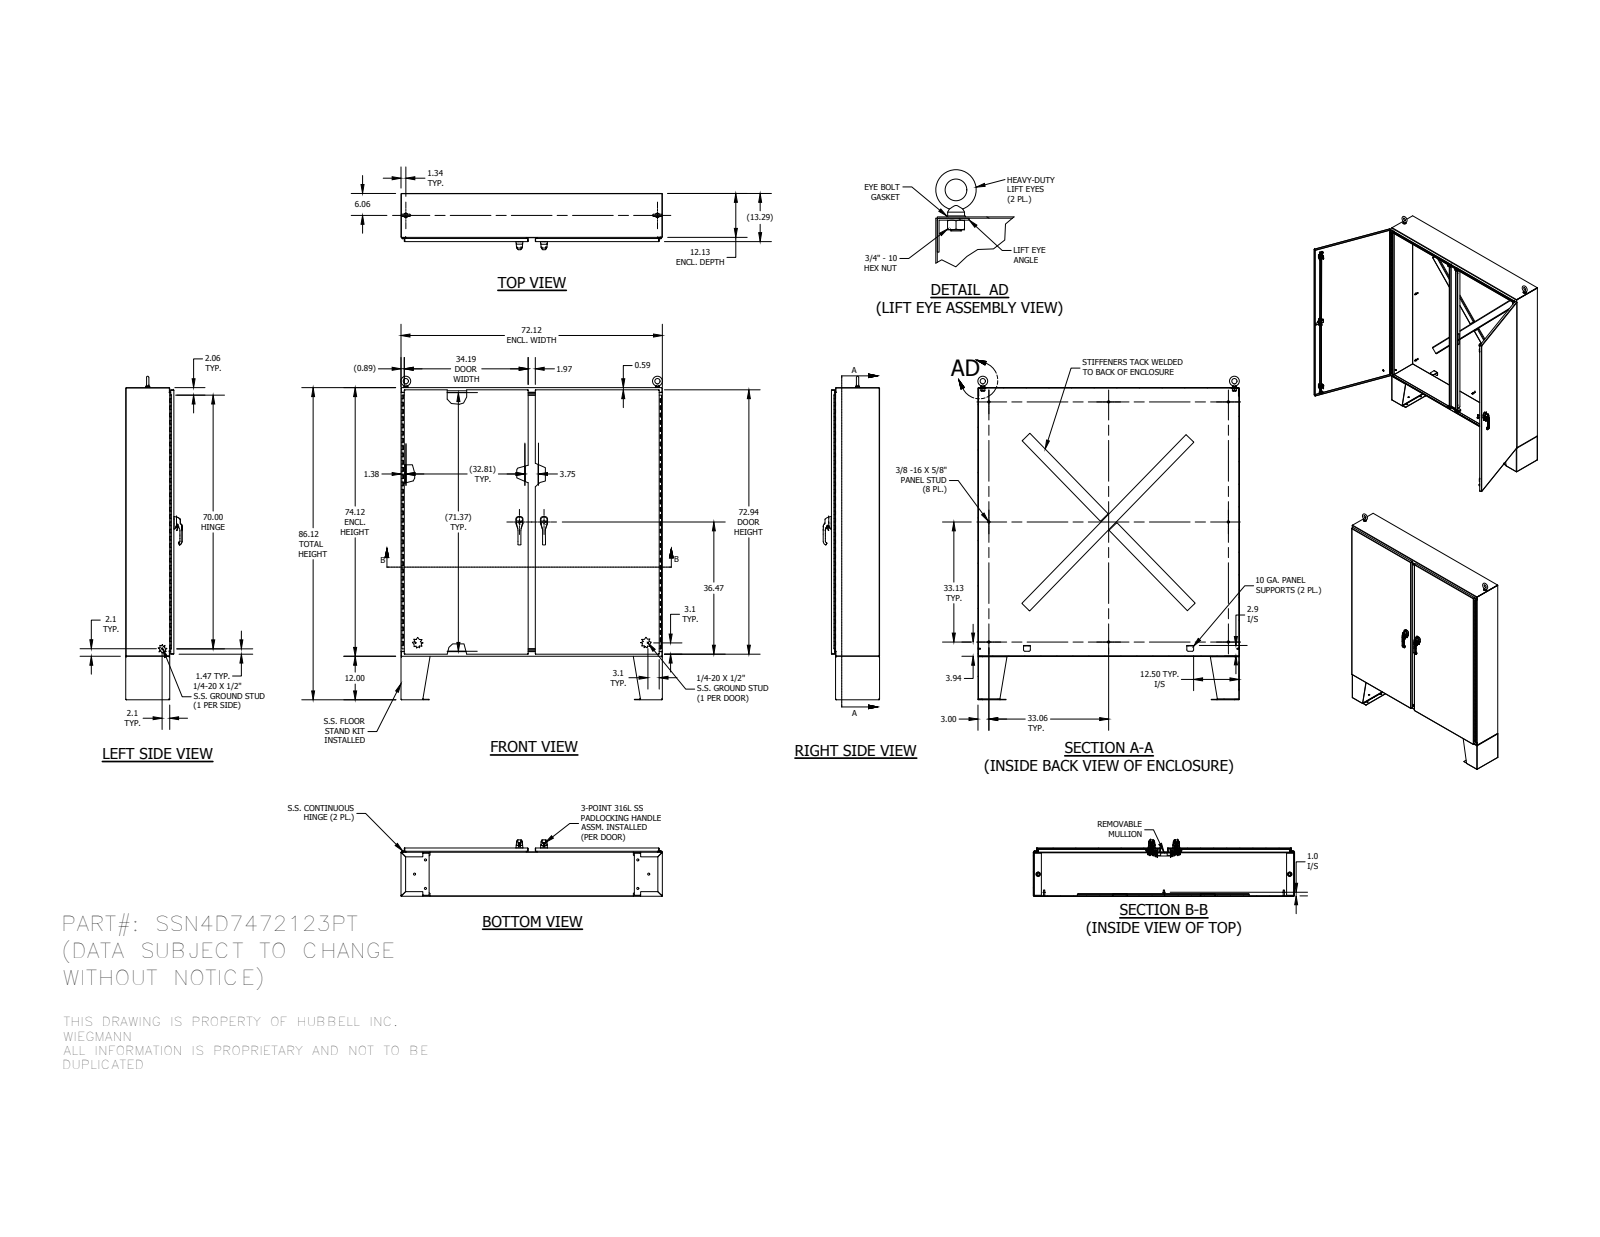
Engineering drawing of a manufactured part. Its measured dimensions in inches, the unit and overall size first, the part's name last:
Units: inches
Overall size (bounding box): 89.248 × 72.125 × 15.538
Round holes (diameter × count): ⌀0.563 ×18, ⌀0.262 ×16, ⌀0.375 ×16, ⌀0.187 ×8, ⌀0.213 ×6, ⌀0.25 ×6, ⌀0.281 ×6, ⌀0.196 ×4, ⌀0.241 ×4, ⌀0.252 ×4, ⌀0.281 ×4, ⌀0.315 ×4
Round bosses / shafts (diameter × count): ⌀0.33 ×10, ⌀0.625 ×8, ⌀0.25 ×7, ⌀1 ×6, ⌀0.533 ×6, ⌀0.236 ×6, ⌀0.563 ×4, ⌀0.531 ×4
Partial cylindrical surfaces — rounded edges, fillets, slot ends (radius × count): R0.02 ×360, R0.012 ×213, R0.019 ×46, R0.125 ×46, R0.05 ×34, R0.031 ×32, R0.079 ×28, R0.025 ×24
Main face-to-face distances: 0.094, 13.193, 13.196, 13.1, 13.102, 13.287, 0.091, 13.29, 0.096, 72.031
Hole centre spacings: 15.556, 0.38, 0.38, 0.76, 7.778, 31.111, 64.052, 64.427
Volume: 1 716 in³ · Surface area: 36 147 in²
Bodies: 138 solids, 7352 faces (2804 planar, 2832 cylindrical, 1716 other)
Part name (STEP PRODUCT): 38626_1; LOCK-NUT_AF0_1; SSN4D74723PTLDR_1; 328131-70_1_1 (+8 more)
STEP written by: SolidWorks 2014 (AUTOMOTIVE_DESIGN)
